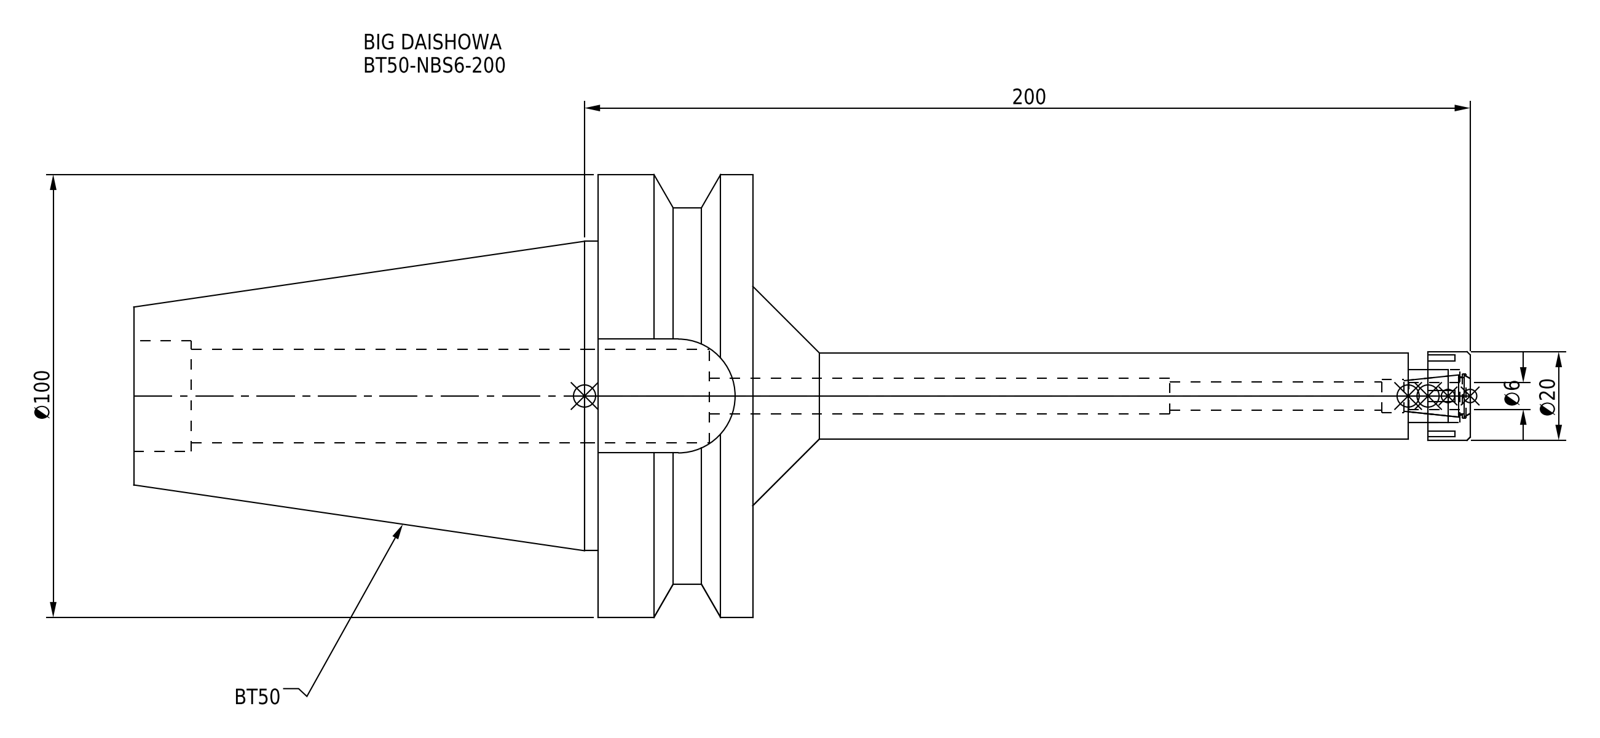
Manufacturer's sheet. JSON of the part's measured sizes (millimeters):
{"part_name": "BT50-NBS6-200; BT50NB06200-060_ASM.stp; NBN6_1.stp; BT50-NBS6-200-FreeParts (+3 more)", "step_written_by": "SolidWorks 2019 (CONFIG_CONTROL_DESIGN)", "units": "millimeters", "bodies": {"solids": 2, "faces": 93, "planar": 45, "cylindrical": 34, "other": 14}, "overall_size": [301.8, 100, 100], "volume_mm3": 496384, "surface_area_mm2": 68549, "round_holes": [[6.4, 1], [7.5, 1], [8, 1], [8.5, 1], [10, 1], [12, 1], [21.2, 1], [25, 1]], "round_bosses_or_shafts": [[100, 1], [85, 1], [69.85, 1], [20, 1], [19.5, 1]], "partial_cylinders_radius": [[12.85, 1]], "face_to_face_distances": [35, 139.8, 104.8, 70.8, 25.7, 9.8, 25.2, 130, 4.5, 162]}
